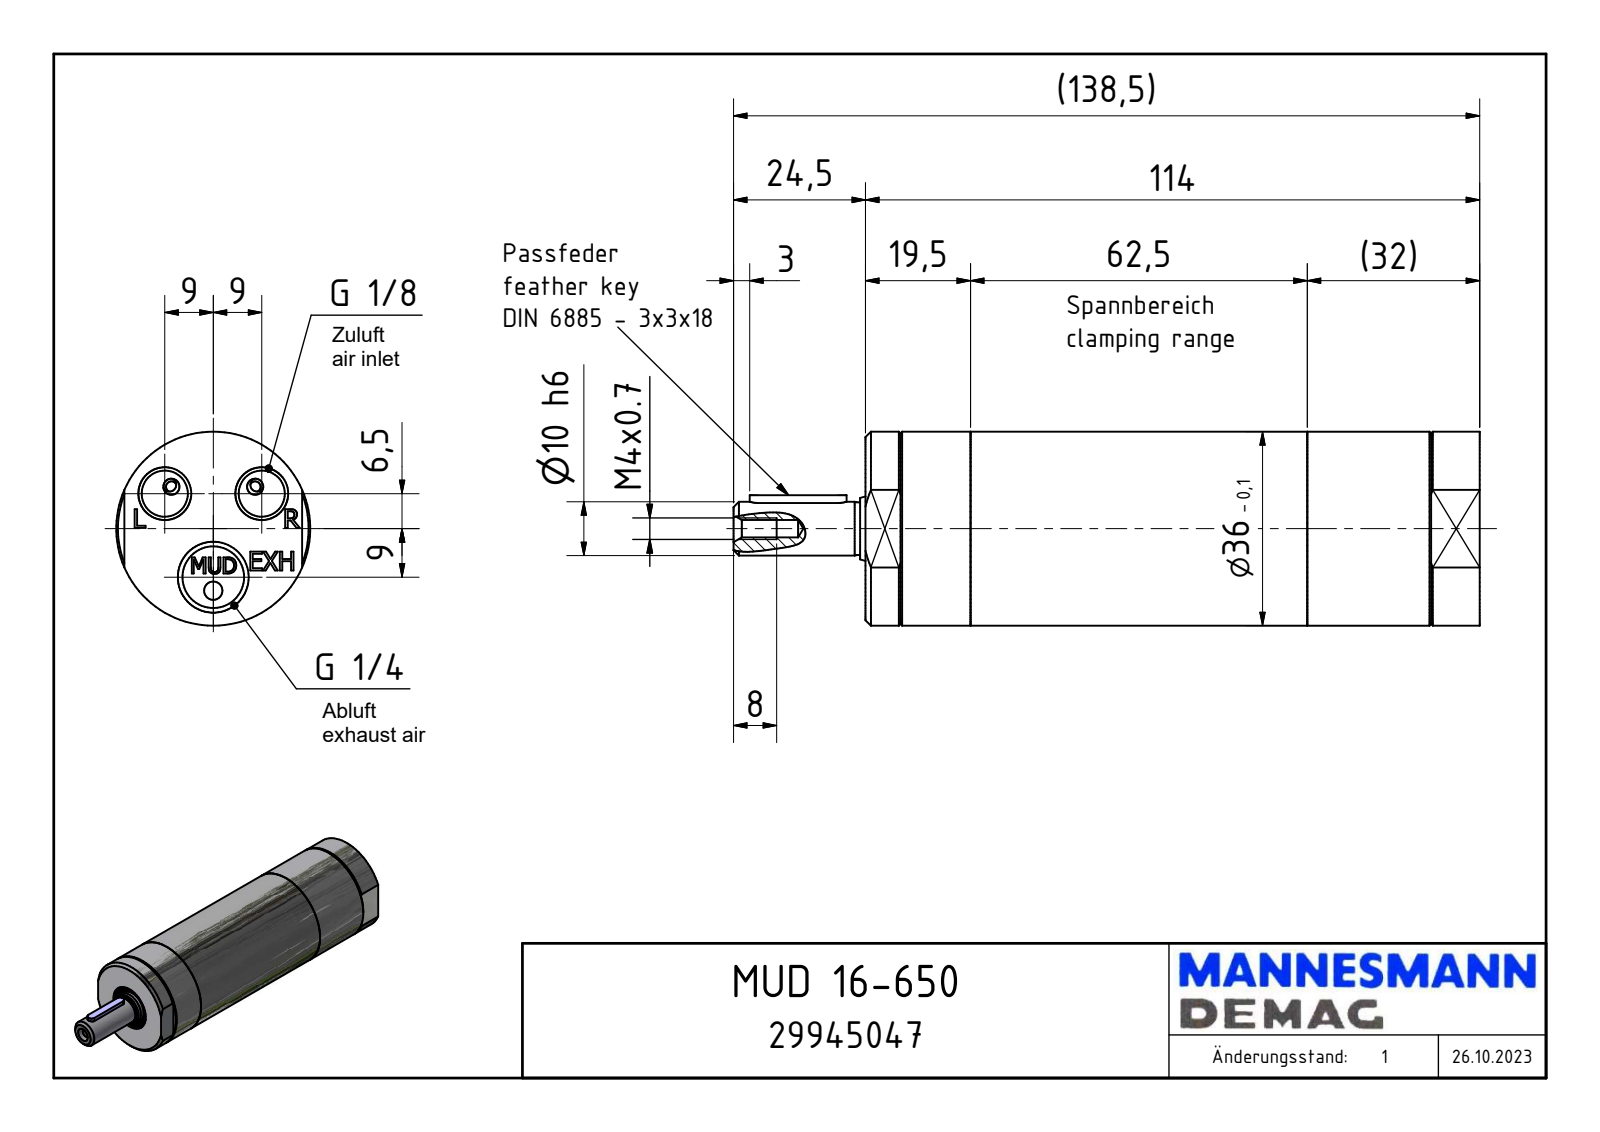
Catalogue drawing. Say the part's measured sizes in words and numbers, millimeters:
The part is named "MUD 16-650_29945047". Its 3-D file was written by "Autodesk Inventor 2024 (AUTOMOTIVE_DESIGN)". It is 1 solid with 120 faces: 78 planar, 17 cylindrical and 25 other. Overall it measures 138.5 by 36 by 36 millimeters. Its volume is 115 154 cubic millimeters and its surface area 16 730 square millimeters. Round holes: 2 of diameter 8.57, 1 of diameter 3.24, 1 of diameter 11.45, 1 of diameter 17. Round bosses or shafts: 1 of diameter 36, 1 of diameter 11.95, 1 of diameter 10, 1 of diameter 9.8. Partial cylindrical surfaces (rounded edges, fillets, slot ends): 2 of radius 1.5. The main face-to-face distances are 114, 33, 104, 10, 0.5, 103.5, 113.5, 15, 18, 1. The hole center spacings are 11.1, 17.92, 9, 18.
